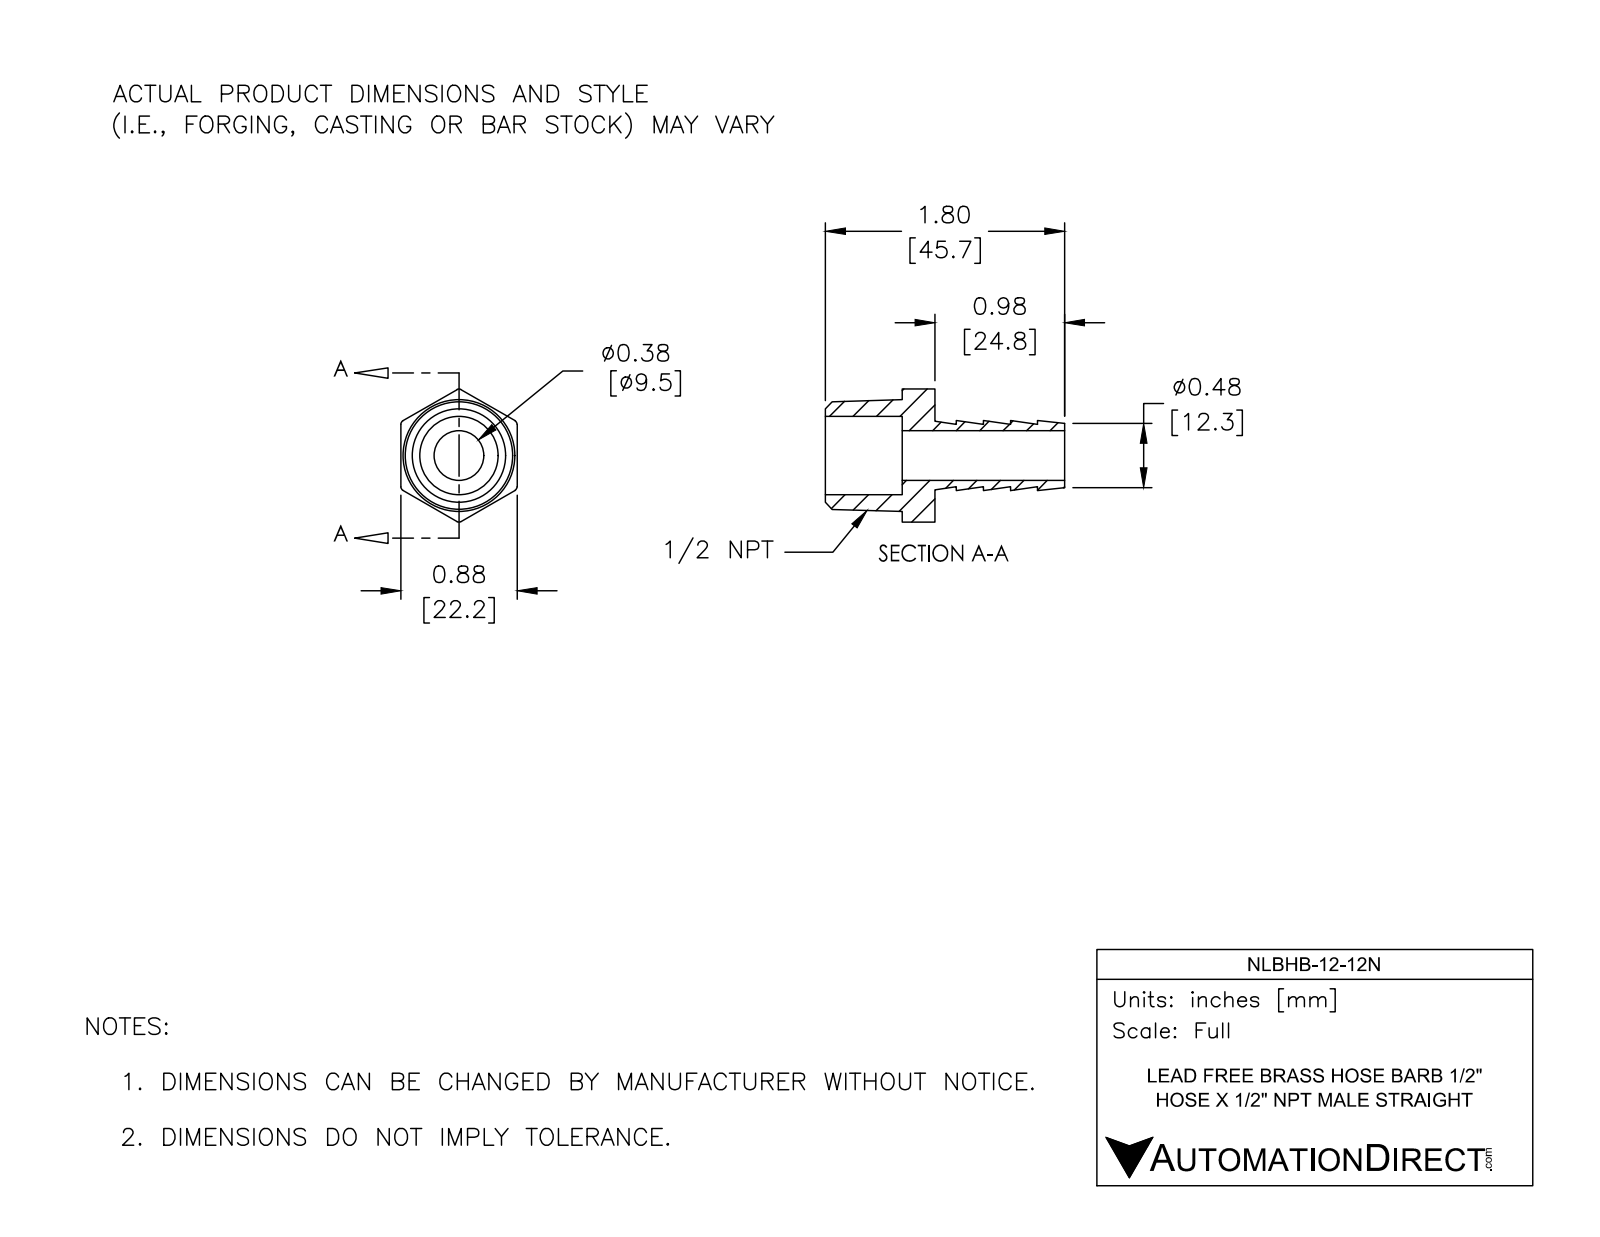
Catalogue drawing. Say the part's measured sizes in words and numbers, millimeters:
The part is named "NLBHB-12-12N". Its 3-D file was written by "SolidWorks 2017 (AUTOMOTIVE_DESIGN)". It is 1 solid with 39 faces: 15 planar, 10 cylindrical and 14 other. Overall it measures 45.7 by 25.4 by 22.2 millimeters. Its volume is 5 980 cubic millimeters and its surface area 4 789 square millimeters. Round holes: 1 of diameter 9.5, 1 of diameter 15. Partial cylindrical surfaces (rounded edges, fillets, slot ends): 6 of radius 0.8. The main face-to-face distances are 22.2, 6.3, 5.2, 20.9, 14.7, 10.4, 15.5, 24.8, 31.1, 45.7.
